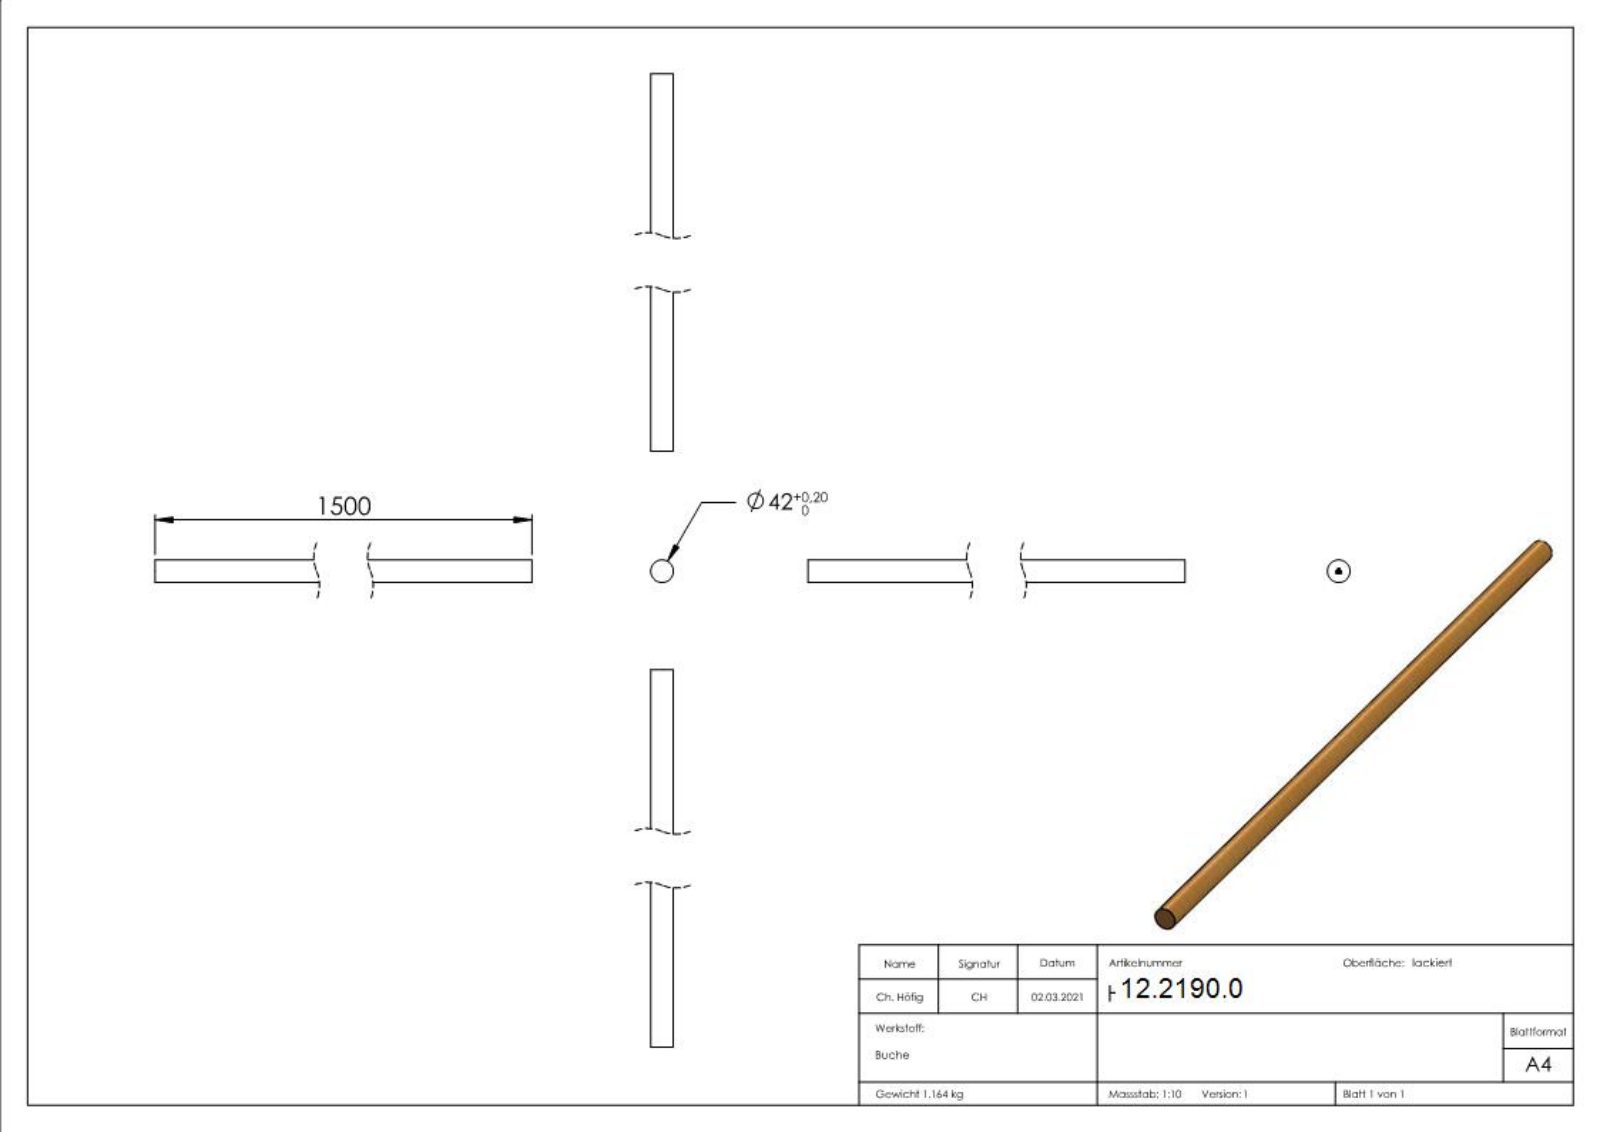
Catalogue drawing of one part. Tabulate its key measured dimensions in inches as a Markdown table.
| quantity | value |
| --- | --- |
| part name | H-BU42-1500 |
| STEP written by | SolidWorks 2018 (CONFIG_CONTROL_DESIGN) |
| units | inches |
| bodies | 1 solid, 288 faces (170 planar, 2 cylindrical, 116 other) |
| overall size | 59.055 × 1.654 × 1.654 |
| volume | 126.8 in³ |
| surface area | 311.1 in² |
| round bosses / shafts (diameter × count) | 1.654 × 1 |
| main face-to-face distances | 59.055, 59.051, 0.088, 0.037, 0.121, 0.059, 0.246, 0.126, 0.25, 0.098 |
